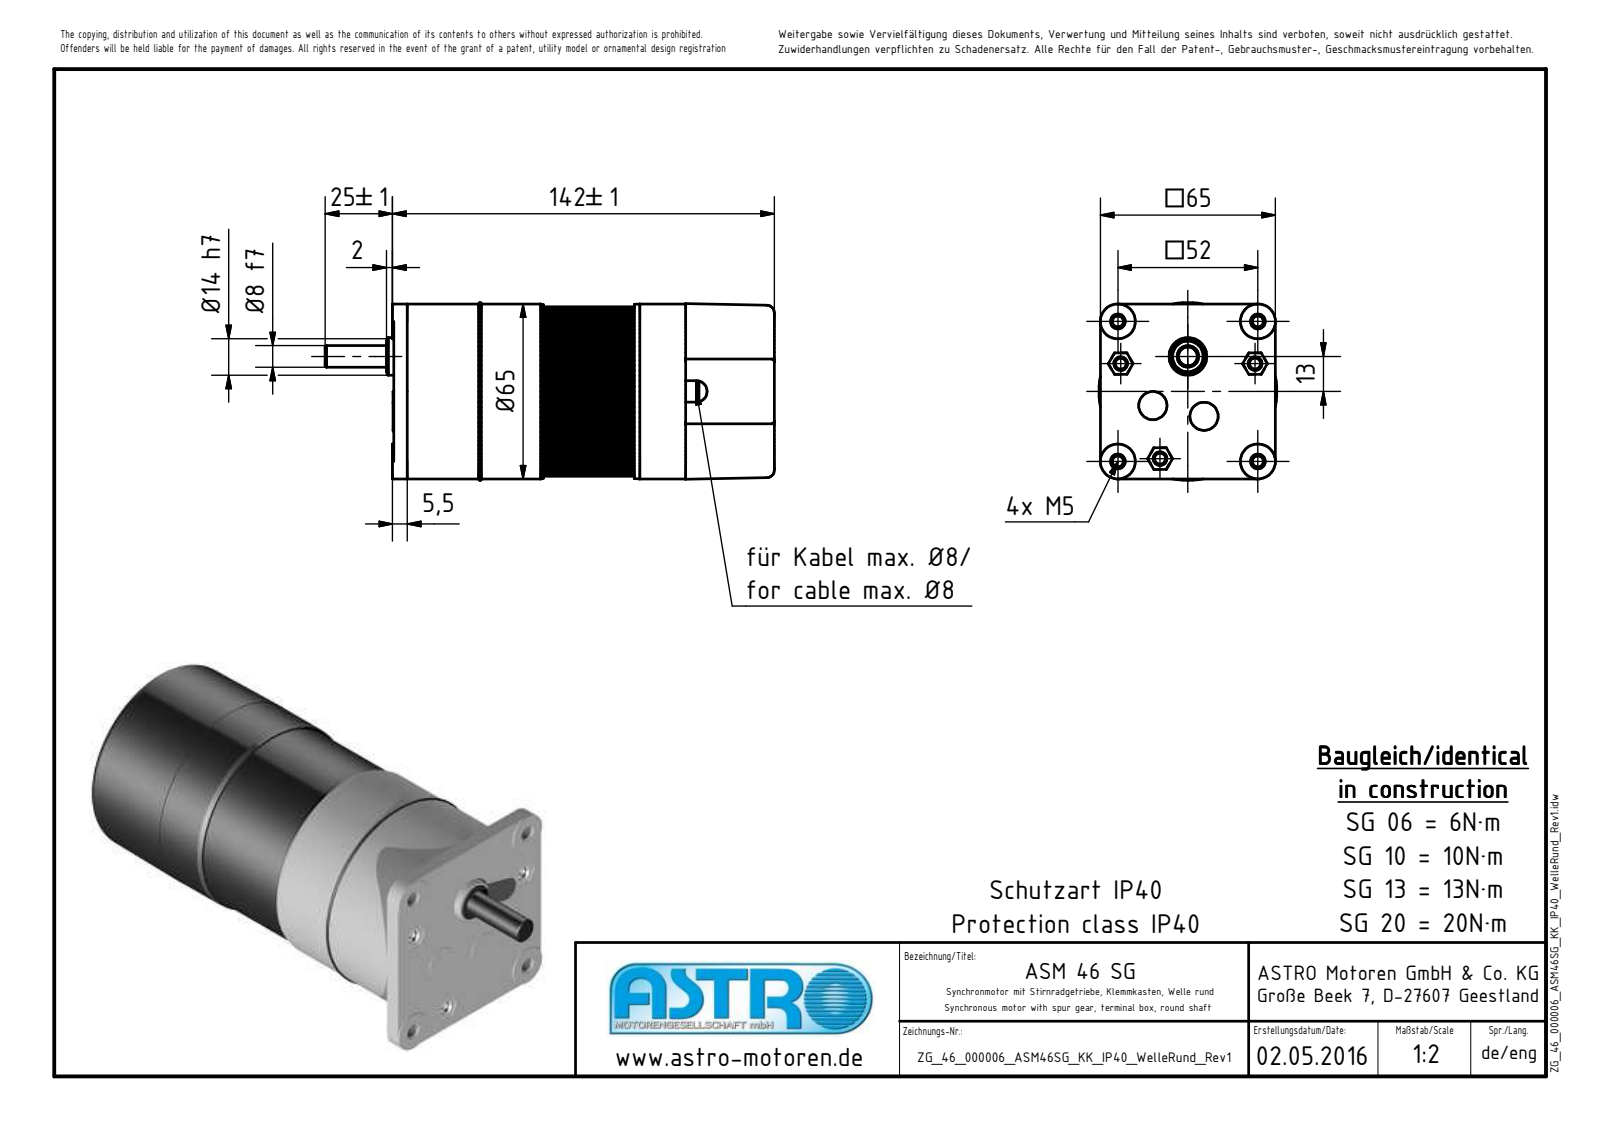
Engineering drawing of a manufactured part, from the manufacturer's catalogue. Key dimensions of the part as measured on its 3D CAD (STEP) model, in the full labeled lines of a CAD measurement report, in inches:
Part name (STEP PRODUCT): ZG_46_000006_ASM46SG_KK_IP40_WelleRund_Rev1; 5101-STG-Metall; LagerschaleB3-ZG-Rev1-0; ZG_51108x067_Endwelle_8x67_Rev0 (+6 more)
STEP written by: Autodesk Inventor 2010 (AUTOMOTIVE_DESIGN)
Units: inches
Bodies: 14 solids, 458 faces (181 planar, 90 cylindrical, 187 other)
Overall size (bounding box): 6.567 × 2.598 × 2.598
Volume: 13.95 in³ · Surface area: 141 in²
Round holes (diameter × count): ⌀0.161 ×8, ⌀0.205 ×3, ⌀0.472 ×2, ⌀0.169 ×1, ⌀0.236 ×1, ⌀0.315 ×1, ⌀0.335 ×1, ⌀0.61 ×1, ⌀0.63 ×1, ⌀2.323 ×1, ⌀2.48 ×1
Round bosses / shafts (diameter × count): ⌀0.512 ×4, ⌀0.157 ×4, ⌀0.143 ×4, ⌀0.473 ×2, ⌀0.413 ×2, ⌀0.335 ×2, ⌀0.118 ×2, ⌀0.098 ×2
Partial cylindrical surfaces — rounded edges, fillets, slot ends (radius × count): R0.02 ×16, R0.039 ×5, R0.207 ×4, R0.157 ×1
Main face-to-face distances: 1.87, 2.067, 2.197, 3.425, 1.555, 0.197, 3.622, 4.264, 4.067, 0.642
Hole centre spacings: 1.063, 1.964, 0.813, 1.503, 1.768, 2.085, 0.415, 0.415
